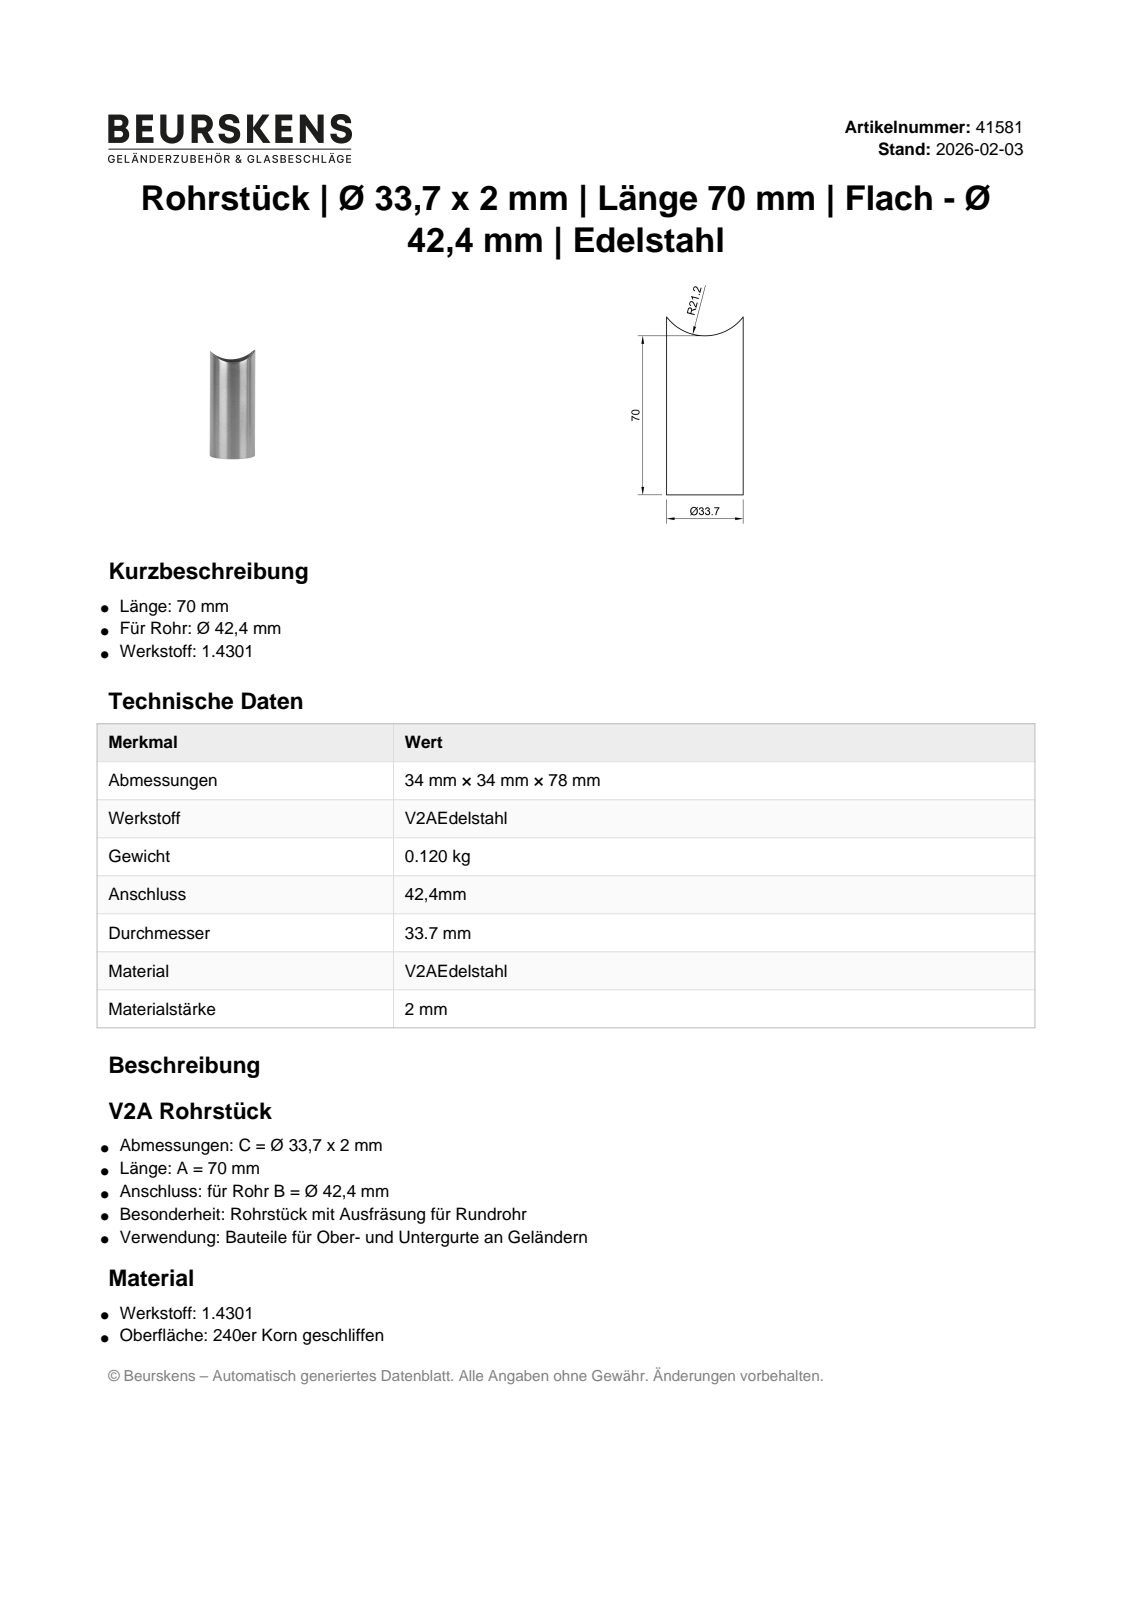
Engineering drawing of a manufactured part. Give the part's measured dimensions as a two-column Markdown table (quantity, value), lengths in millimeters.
| quantity | value |
| --- | --- |
| part name | 41581 |
| STEP written by | Autodesk Inventor 2022 (AUTOMOTIVE_DESIGN) |
| units | millimeters |
| bodies | 1 solid, 4 faces (1 planar, 3 cylindrical, 0 other) |
| overall size | 78.33 × 33.7 × 33.7 |
| volume | 7 563 mm³ |
| surface area | 15 363 mm² |
| round holes (diameter × count) | 31.7 × 1 |
| round bosses / shafts (diameter × count) | 33.7 × 1 |
| partial cylindrical surfaces (radius × count) | 21.2 × 1 |
